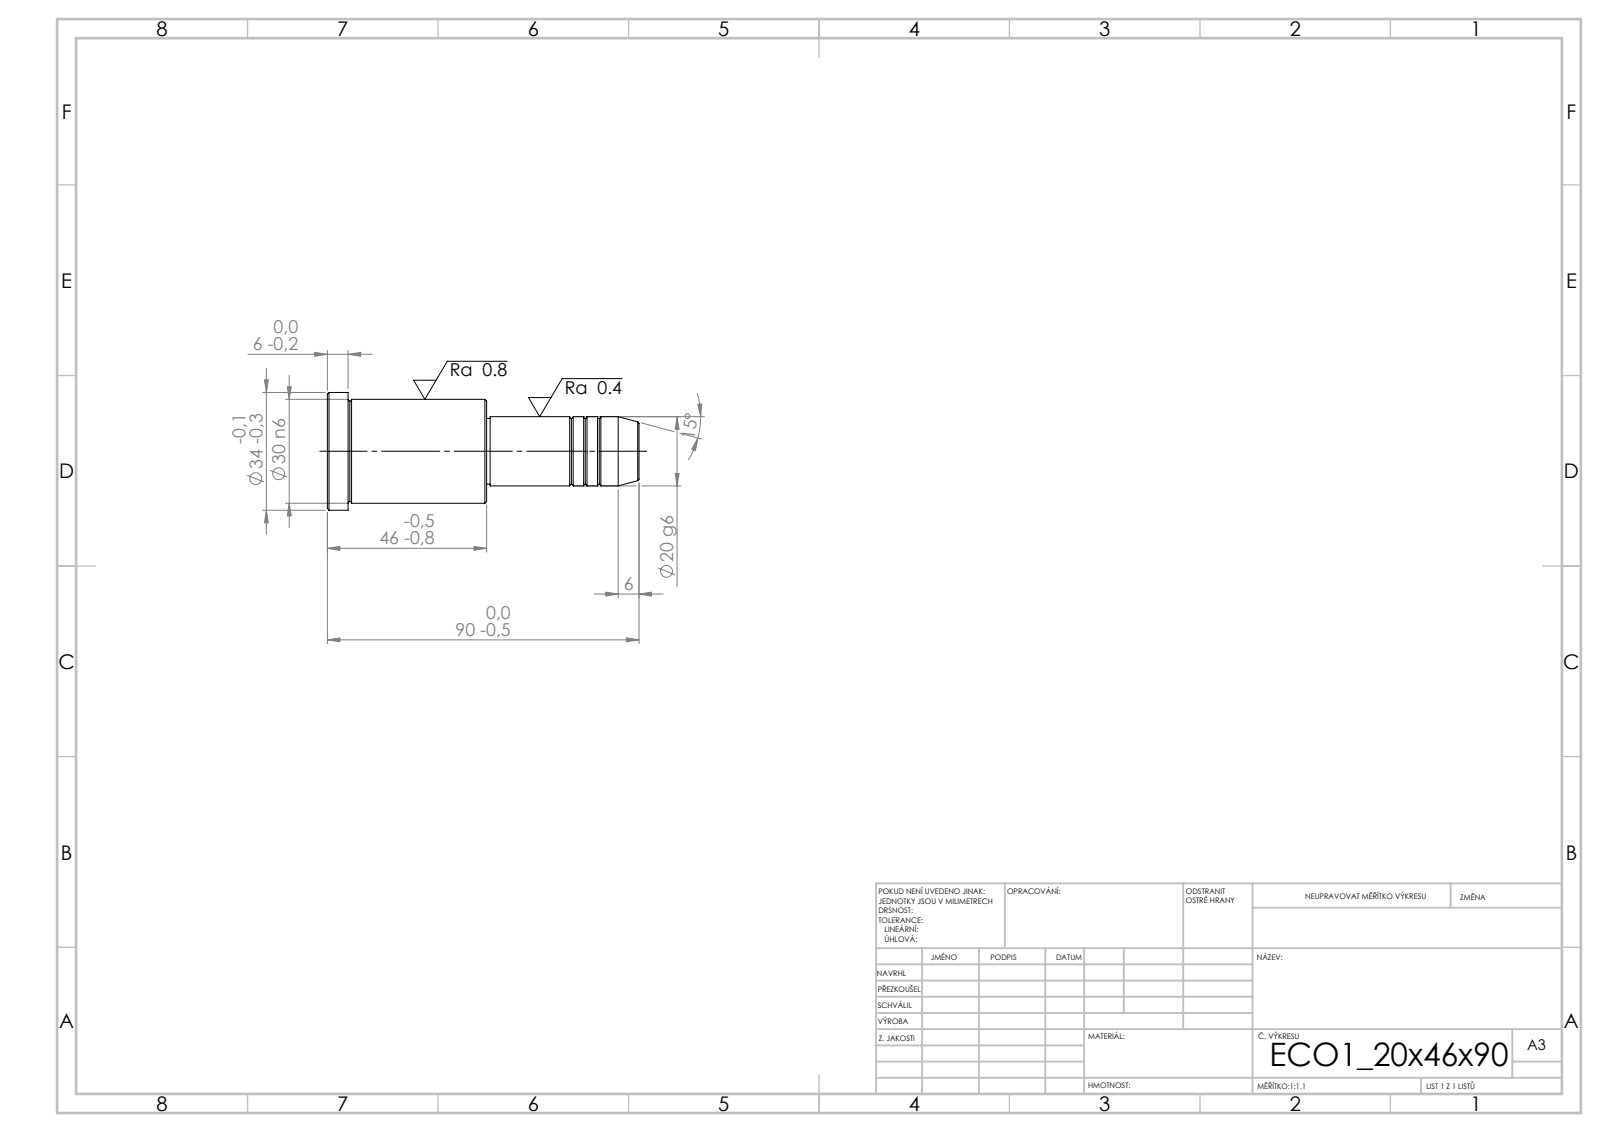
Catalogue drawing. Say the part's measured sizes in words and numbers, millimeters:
Its 3-D file was written by "SolidWorks 2019 (CONFIG_CONTROL_DESIGN)". It is 1 solid with 43 faces: 5 planar, 14 cylindrical and 24 other. Overall it measures 90 by 34 by 34 millimeters. Its volume is 47 092 cubic millimeters and its surface area 9 022 square millimeters. Round bosses or shafts: 1 of diameter 34, 1 of diameter 30, 1 of diameter 20, 1 of diameter 19. The main face-to-face distances are 46, 44, 90, 84, 40, 6, 43, 1, 41, 47.
